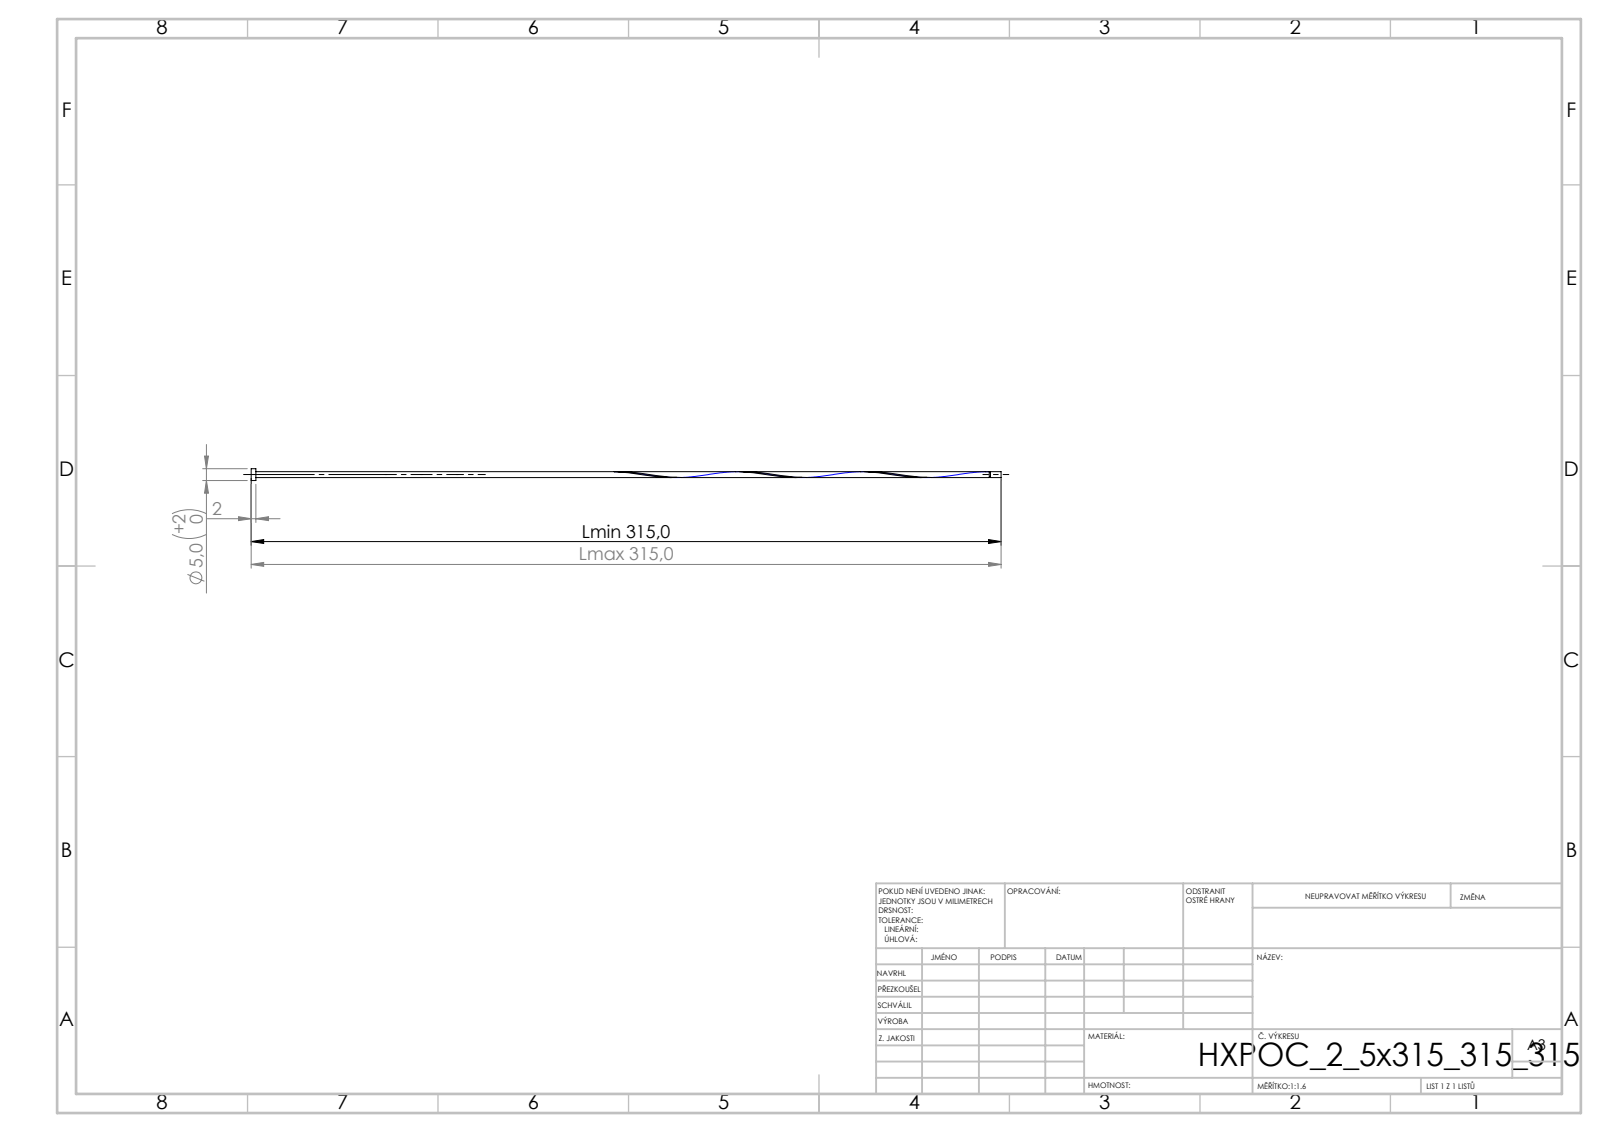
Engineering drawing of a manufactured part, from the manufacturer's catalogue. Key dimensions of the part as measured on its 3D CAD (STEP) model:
STEP written by: SolidWorks 2019 (CONFIG_CONTROL_DESIGN)
Units: millimetres
Bodies: 1 solid, 16 faces (6 planar, 9 cylindrical, 1 other)
Overall size (bounding box): 315 × 5 × 5
Volume: 1 904 mm³ · Surface area: 3 394 mm²
Round bosses / shafts (diameter × count): ⌀5 ×1, ⌀2.5 ×1, ⌀2 ×1
Main face-to-face distances: 2, 315, 313, 310.5, 308.5, 4.5, 310, 308, 0.5, 5
